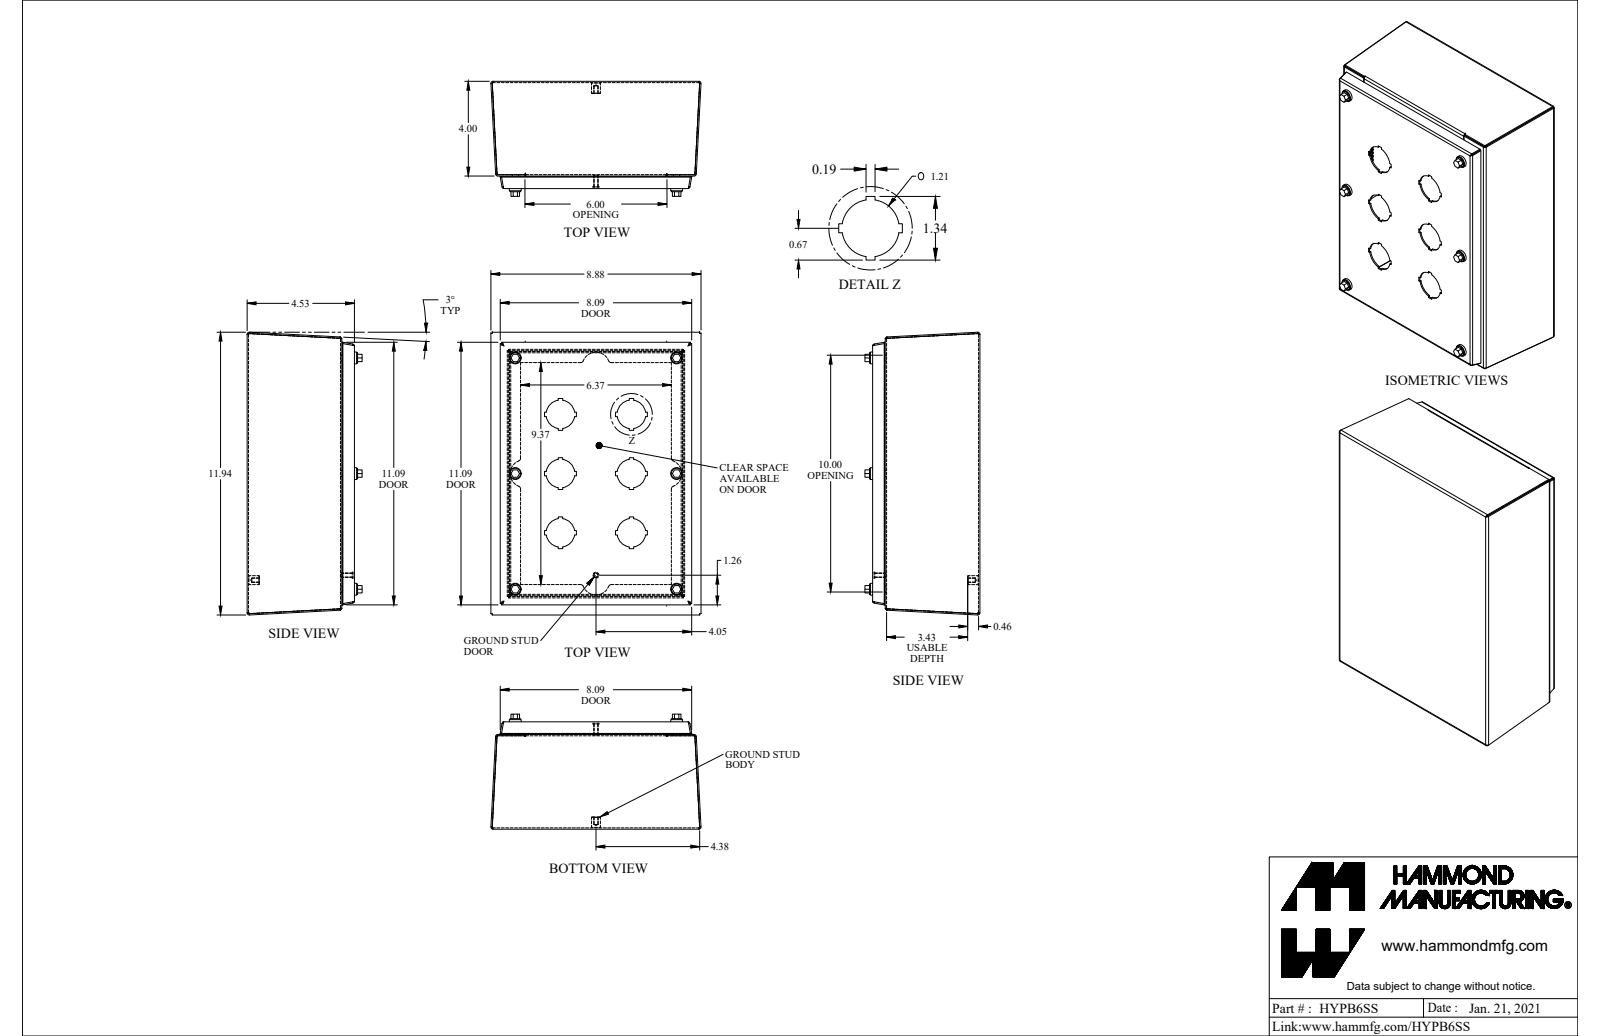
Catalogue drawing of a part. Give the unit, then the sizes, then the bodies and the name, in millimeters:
Units: millimetres
Overall size (bounding box): 303.3 × 228 × 123.4
Round holes (diameter × count): ⌀1.7 ×6, ⌀6 ×6, ⌀6.1 ×6, ⌀6.1 ×6, ⌀6.4 ×6, ⌀6.4 ×6, ⌀30.7 ×6, ⌀10.2 ×4, ⌀4 ×1
Round bosses / shafts (diameter × count): ⌀9.5 ×7, ⌀4.8 ×7, ⌀12.7 ×6, ⌀11.4 ×6, ⌀10.3 ×6, ⌀8 ×6, ⌀6.4 ×1
Partial cylindrical surfaces — rounded edges, fillets, slot ends (radius × count): R0.7 ×16, R2.2 ×16, R3.2 ×8, R1.9 ×6, R1.4 ×4, R12.7 ×4, R14.6 ×4
Main face-to-face distances: 1.4, 112.2, 113.7, 1.4, 115.1, 113.7, 100.2, 12.1, 101.6, 13.5
Hole centre spacings: 302.5, 77.6, 124, 138.6, 173.2, 213, 248.1, 124
Volume: 490 600 mm³ · Surface area: 626 500 mm²
Bodies: 30 solids, 629 faces (418 planar, 186 cylindrical, 25 other)
Part name (STEP PRODUCT): HYPB6SS
STEP written by: SolidWorks 2021 (AUTOMOTIVE_DESIGN)
